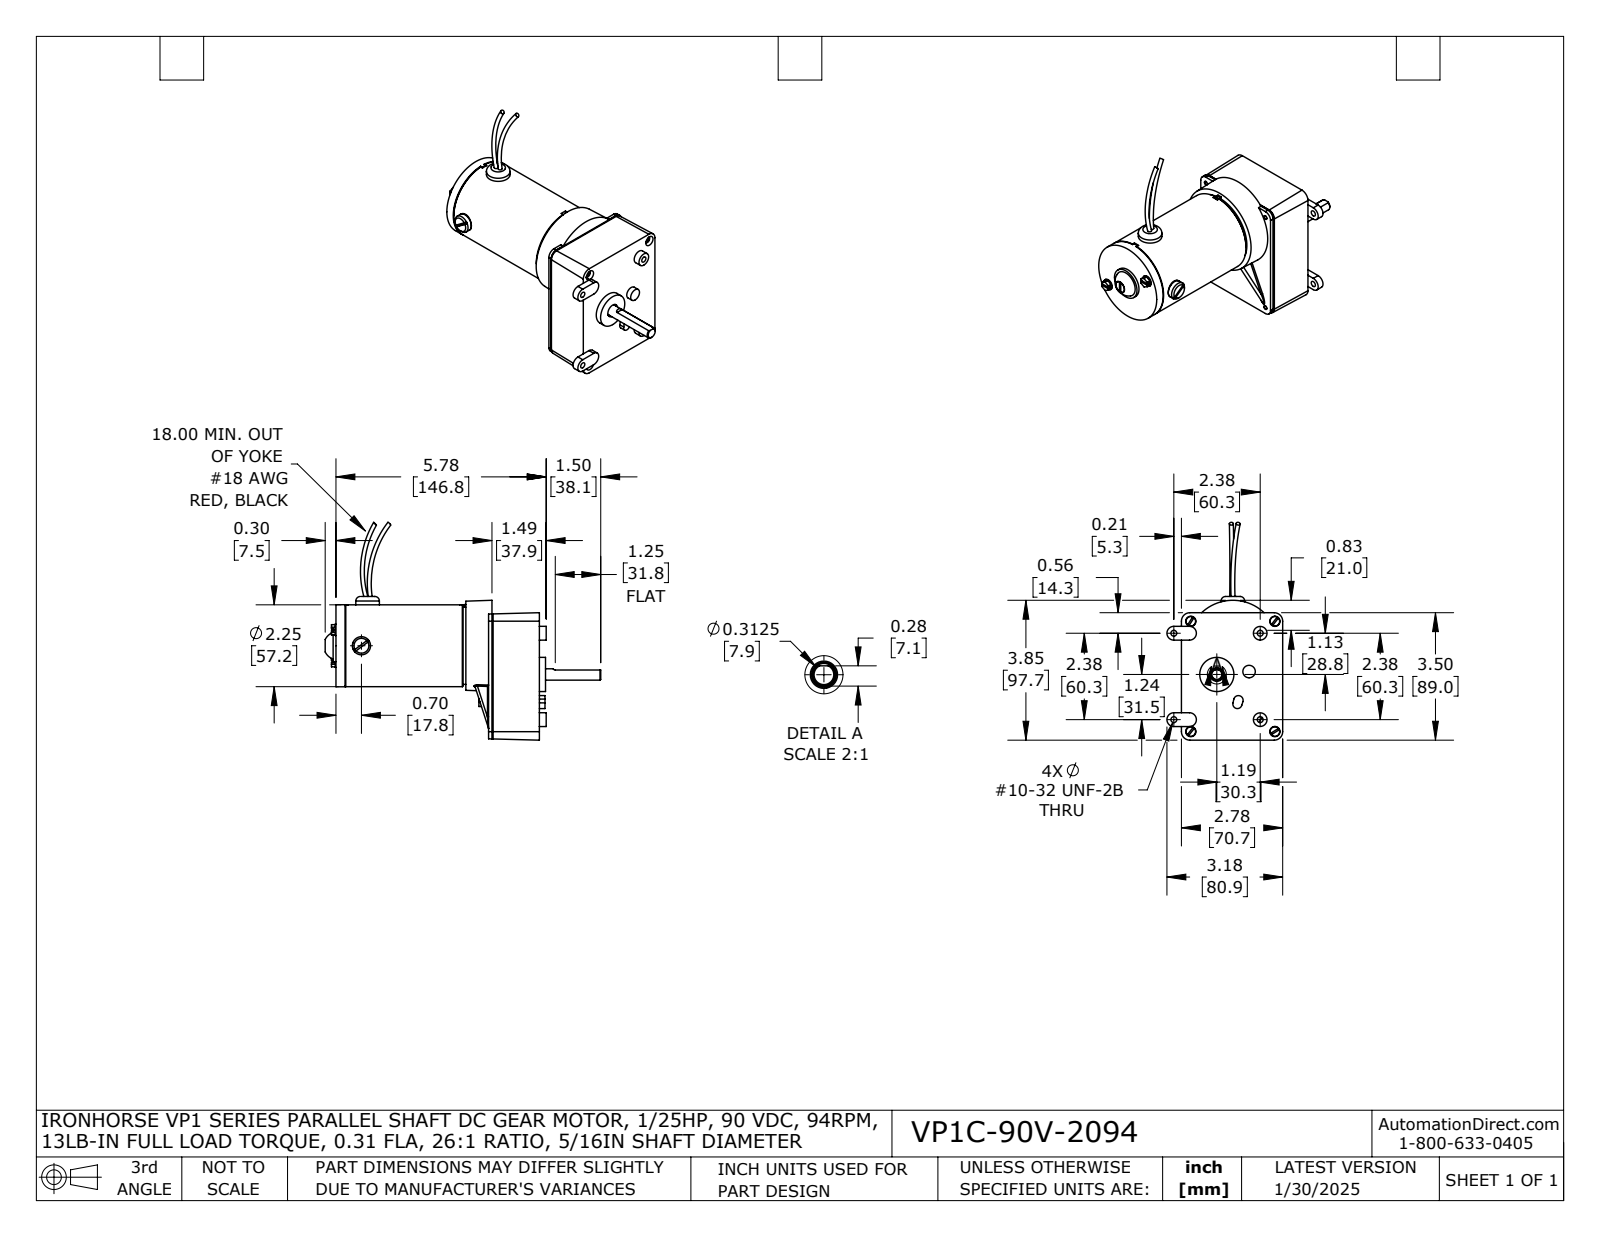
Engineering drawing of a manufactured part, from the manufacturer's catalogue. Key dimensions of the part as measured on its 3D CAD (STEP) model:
Part name (STEP PRODUCT): VP1C-90V-2094
STEP written by: SolidWorks 2021 (AUTOMOTIVE_DESIGN)
Units: inches
Bodies: 34 solids, 1338 faces (477 planar, 580 cylindrical, 281 other)
Overall size (bounding box): 7.578 × 5.989 × 3.183
Volume: 13.71 in³ · Surface area: 226.6 in²
Round holes (diameter × count): ⌀0.281 ×7, ⌀0.037 ×4, ⌀0.117 ×4, ⌀0.149 ×4, ⌀0.15 ×4, ⌀0.161 ×4, ⌀0.125 ×2, ⌀0.187 ×2, ⌀0.127 ×1, ⌀0.127 ×1, ⌀0.213 ×1, ⌀0.239 ×1
Round bosses / shafts (diameter × count): ⌀0.136 ×4, ⌀0.313 ×3, ⌀0.375 ×2, ⌀2.256 ×1, ⌀2.25 ×1, ⌀2.123 ×1, ⌀2.003 ×1, ⌀2 ×1
Partial cylindrical surfaces — rounded edges, fillets, slot ends (radius × count): R0.028 ×24, R0.051 ×24, R0.02 ×12, R0.055 ×12, R0.058 ×12, R0.03 ×8, R0.031 ×8, R0.19 ×8
Main face-to-face distances: 1.304, 0.097, 1.207, 1.397, 1.3, 0.093, 1.273, 1.176, 0.031, 0.124
Hole centre spacings: 0.875, 0.77, 1.936, 2.31, 2.312, 3.03, 3.031, 0.135
